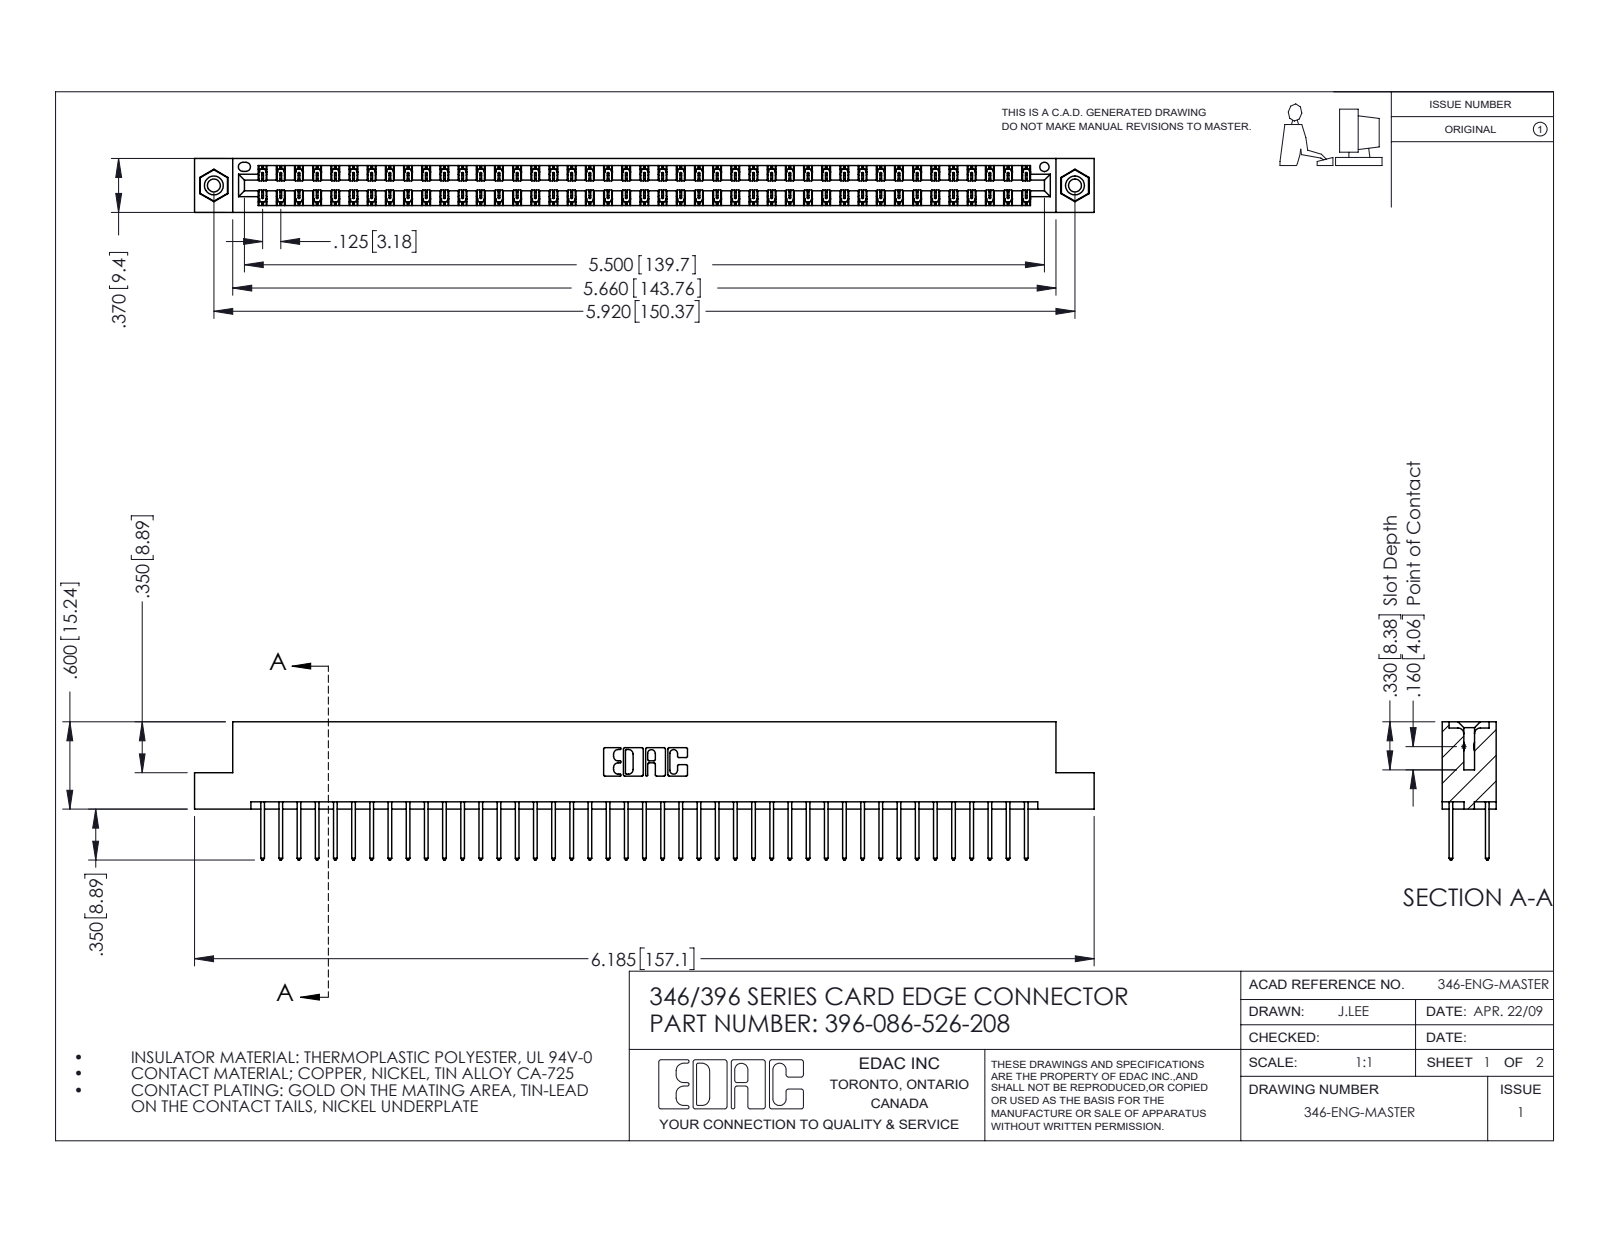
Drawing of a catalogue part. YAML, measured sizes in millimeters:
part_name: "345-250-001_345-250-003-102; 396-086-526-208; 345-292-001_345-293-126; 346 Part_Flush Mounting Lugs - 0.156 Dia-TI"
step_written_by: "SolidWorks 2016 (CONFIG_CONTROL_DESIGN)"
units: millimeters
bodies: {solids: 89, faces: 4654, planar: 3118, cylindrical: 1520, other: 16}
overall_size: [157.1, 24.1, 9.4]
volume: 15500
surface_area: 21920
round_holes:
  - {diameter: 2.3, count: 2}
  - {diameter: 3.2, count: 2}
  - {diameter: 4, count: 2}
  - {diameter: 1.6, count: 1}
round_bosses_or_shafts:
  - {diameter: 3.9, count: 2}
partial_cylinders:
  - {radius: 0.2, count: 129}
  - {radius: 0.3, count: 86}
  - {radius: 0.3, count: 22}
  - {radius: 0.2, count: 6}
  - {radius: 0.8, count: 6}
  - {radius: 0.7, count: 3}
  - {radius: 0.4, count: 2}
  - {radius: 0.6, count: 2}
face_to_face_distances: [1.2, 8.2, 6.4, 9.4, 1.8, 7.6, 0.6, 7, 3.8, 5.6]
hole_center_spacings: [6.2, 145.1, 150.4]
